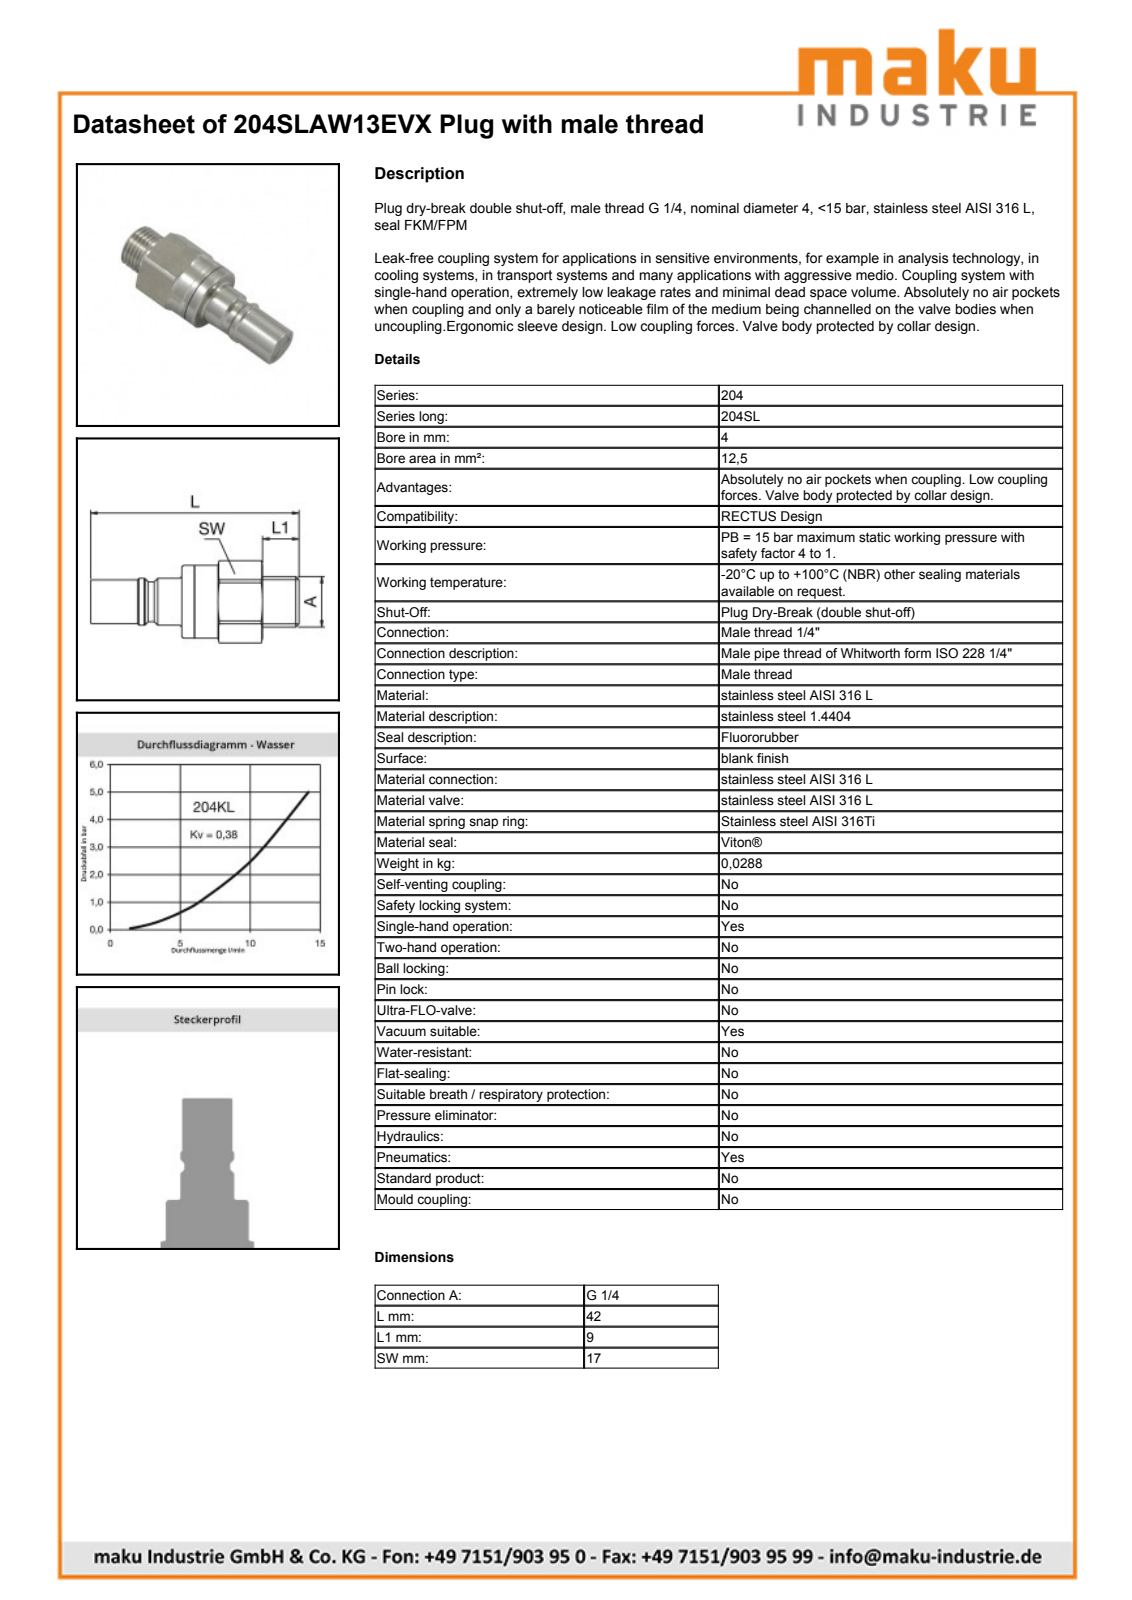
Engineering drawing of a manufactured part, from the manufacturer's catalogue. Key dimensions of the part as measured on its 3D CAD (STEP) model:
Part name (STEP PRODUCT): D110030
STEP written by: Autodesk Inventor 2013 (AUTOMOTIVE_DESIGN)
Units: millimetres
Bodies: 1 solid, 68 faces (15 planar, 19 cylindrical, 34 other)
Overall size (bounding box): 41.9 × 19.03 × 18.17
Volume: 5 287 mm³ · Surface area: 2 435 mm²
Round holes (diameter × count): ⌀7.6 ×1, ⌀12 ×1
Round bosses / shafts (diameter × count): ⌀14 ×1, ⌀13.16 ×1, ⌀11.4 ×1, ⌀9 ×1, ⌀8.4 ×1, ⌀6.78 ×1
Partial cylindrical surfaces — rounded edges, fillets, slot ends (radius × count): R9.57 ×1
Main face-to-face distances: 17, 9, 8.55, 17.55, 6.85, 15.4, 24.4, 17.5, 24.35, 32.9
